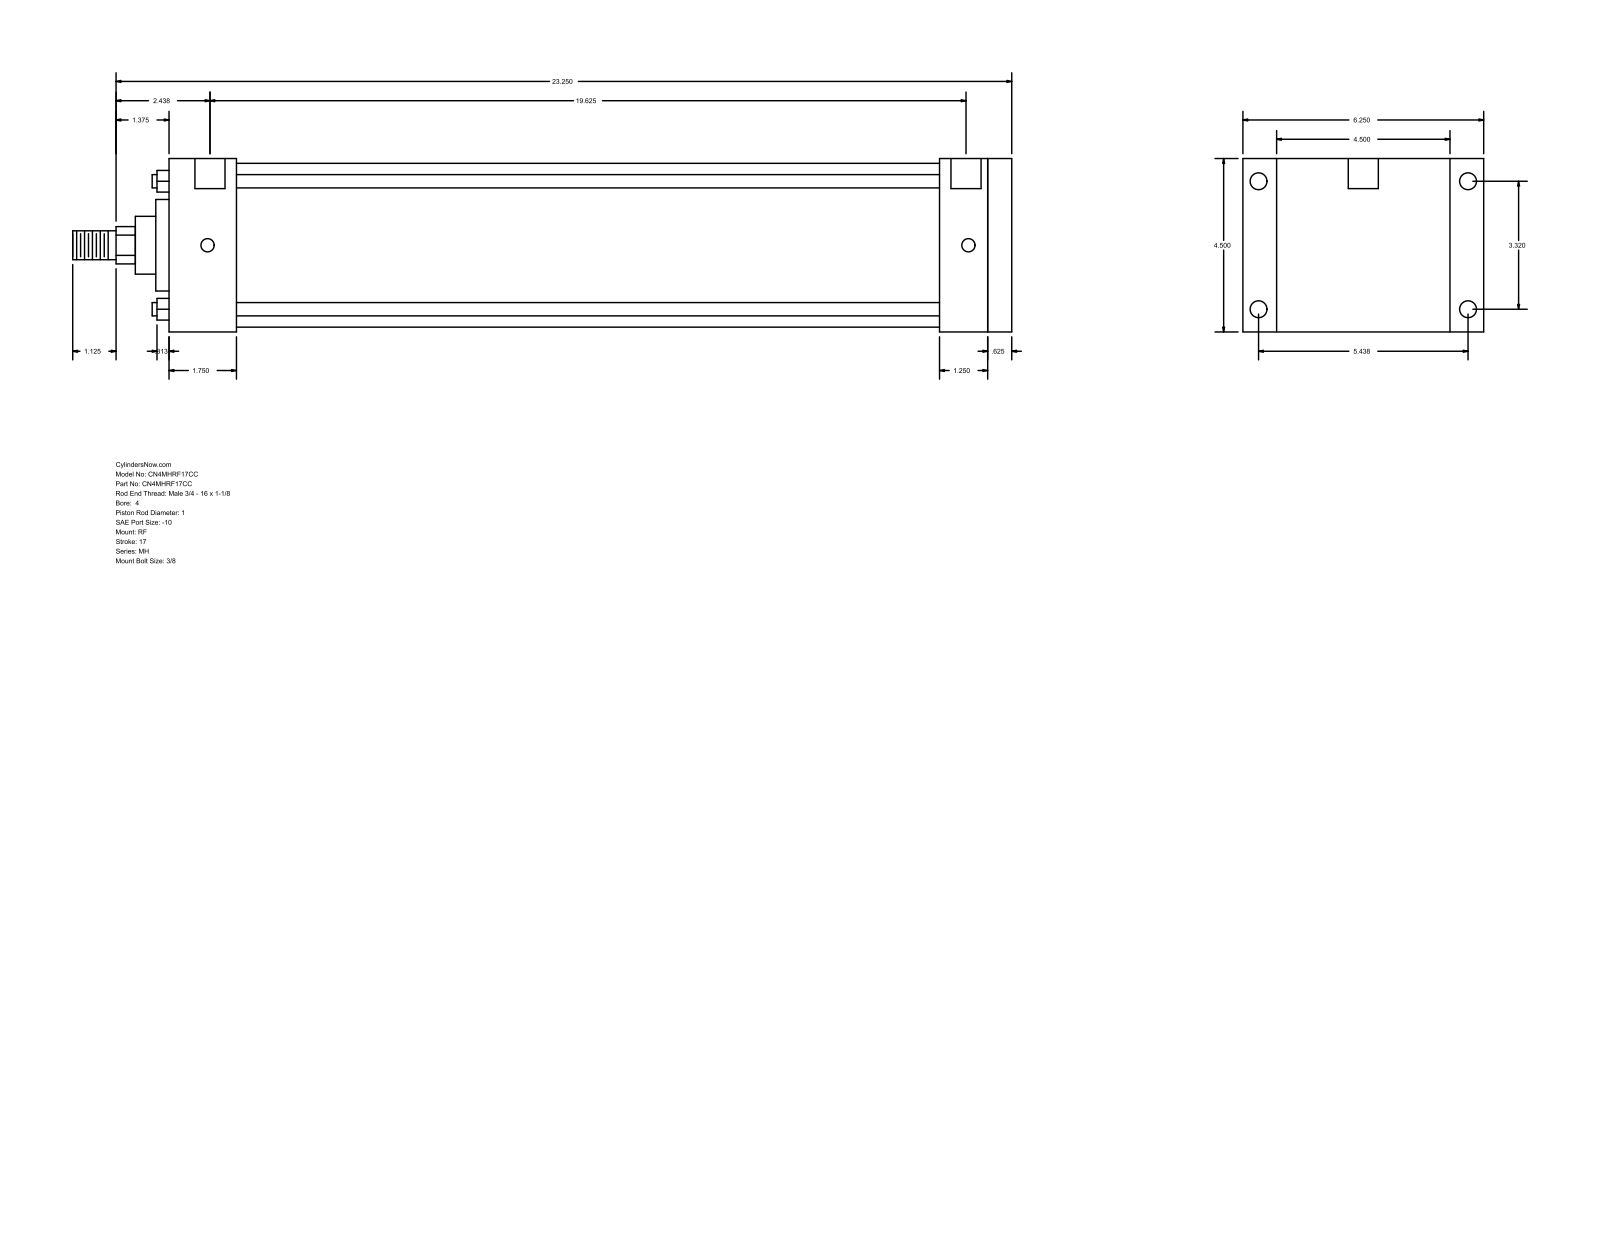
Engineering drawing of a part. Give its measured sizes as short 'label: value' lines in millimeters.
name: MH_RF__0400_1
written by: GSSL Pune (CONFIG_CONTROL_DESIGN)
unit: mm
bodies: 0 solids, 94 faces (65 planar, 29 cylindrical, 0 other)
size: 619.12 × 158.75 × 114.3
holes: 4× ⌀8.73, 4× ⌀11.13, 2× ⌀19.84
bosses: 4× ⌀8.76, 1× ⌀107.95, 1× ⌀60.33, 1× ⌀38.1, 1× ⌀25.4, 1× ⌀19.05
rounds: 1× R12.29
face distances: 114.3, 555.63, 539.75, 15.88, 47.63, 44.46, 495.29, 511.17, 508, 463.54
hole spacings: 84.32, 138.12, 161.82, 501.65, 1.58, 1.59, 498.48, 500.06
